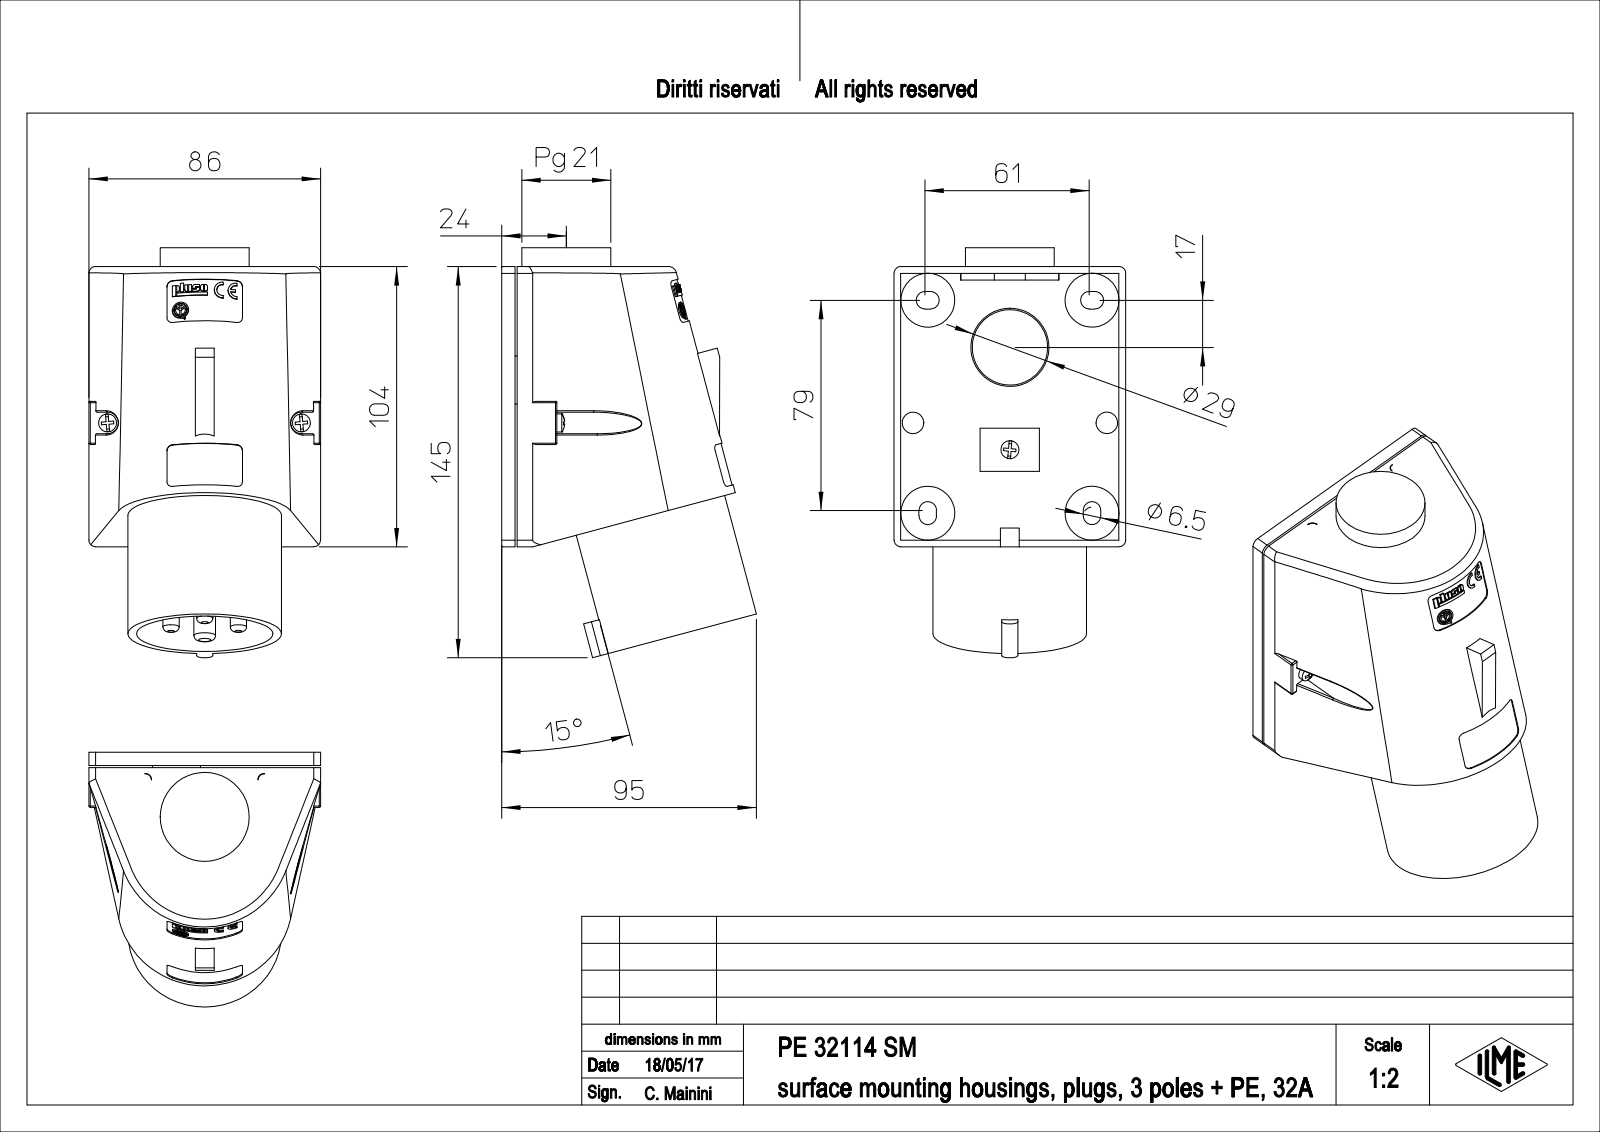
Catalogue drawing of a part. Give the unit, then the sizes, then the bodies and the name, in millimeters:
Units: millimetres
Overall size (bounding box): 152.14 × 94.53 × 86
Round holes (diameter × count): ⌀6.1 ×3, ⌀2.8 ×2, ⌀3.2 ×2, ⌀4.5 ×2, ⌀4.2 ×1, ⌀5.04 ×1, ⌀27.54 ×1, ⌀29 ×1, ⌀32 ×1, ⌀50.6 ×1
Round bosses / shafts (diameter × count): ⌀6.7 ×5, ⌀20 ×4, ⌀6 ×4, ⌀8 ×3, ⌀57 ×1, ⌀50 ×1, ⌀33 ×1, ⌀17.8 ×1
Partial cylindrical surfaces — rounded edges, fillets, slot ends (radius × count): R0.5 ×18, R0.17 ×11, R2 ×10, R0.86 ×9, R3.25 ×8, R2.5 ×6, R0.3 ×3, R3 ×3
Main face-to-face distances: 0.8, 3.95, 4.75, 1, 7, 2.25, 4.95, 5.75, 3.05, 2.5
Hole centre spacings: 12.5, 17.68, 37.36, 45.61, 72, 12.51, 25, 37.29
Volume: 494 999 mm³ · Surface area: 90 100 mm²
Bodies: 1 solid, 1005 faces (645 planar, 203 cylindrical, 157 other)
Part name (STEP PRODUCT): PE_32114_SM
STEP written by: PTC Creo Elements/Direct Modeling 19.0E 27-Jun-2016 (C) Parametric Technology GmbH (AUTOMOTIVE_DESIGN)
